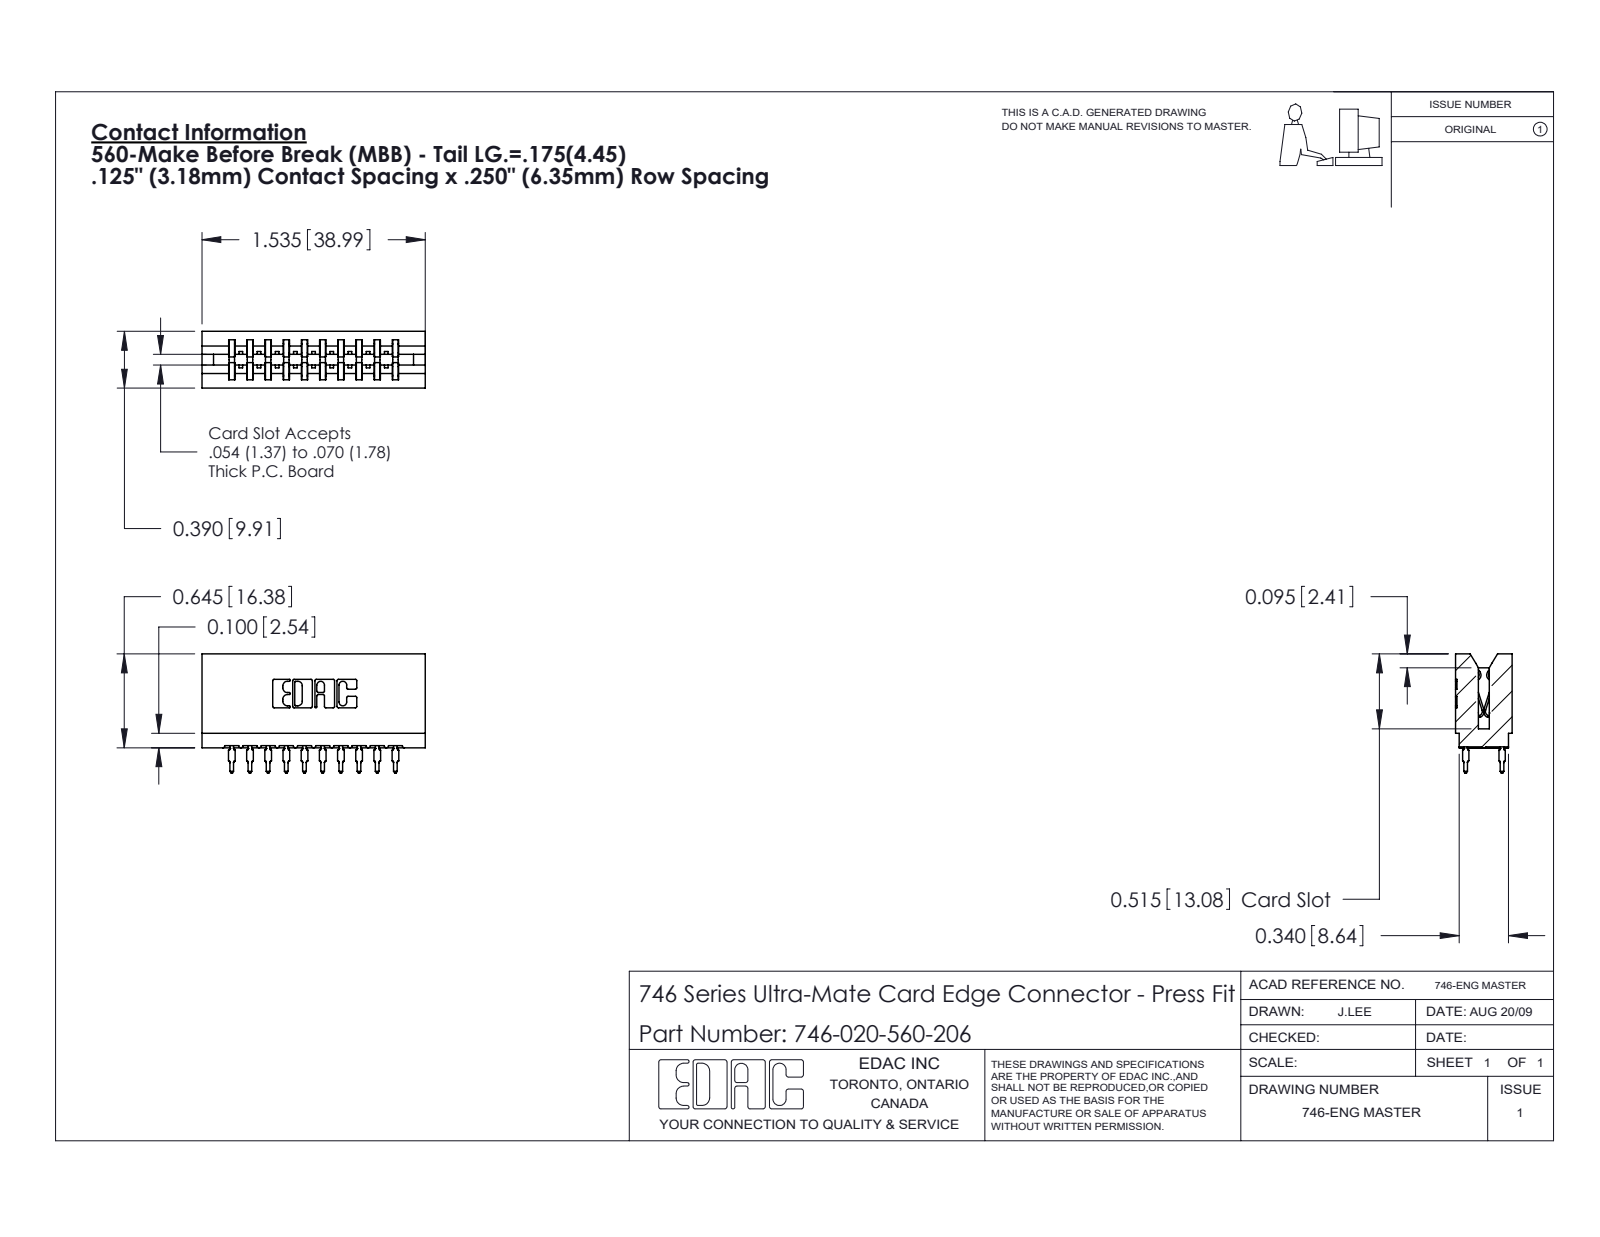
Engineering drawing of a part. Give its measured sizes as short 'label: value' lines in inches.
name: 746-020-560-206; 746 Part_.515 Slot Depth - 06; 746-292-001_560
written by: SolidWorks 2020 (CONFIG_CONTROL_DESIGN)
unit: in
bodies: 21 solids, 1988 faces (996 planar, 472 cylindrical, 520 other)
size: 1.535 × 0.819 × 0.39
volume: 0.271 in³; area: 10.66 in²
rounds: 40× R0.021, 22× R0.01, 11× R0.015, 8× R0.005, 8× R0.011, 6× R0.007, 6× R0.031, 4× R0.02
face distances: 0.25, 0.333, 0.057, 0.5, 0.042, 0.125, 0.292, 0.75, 0.39, 0.375
